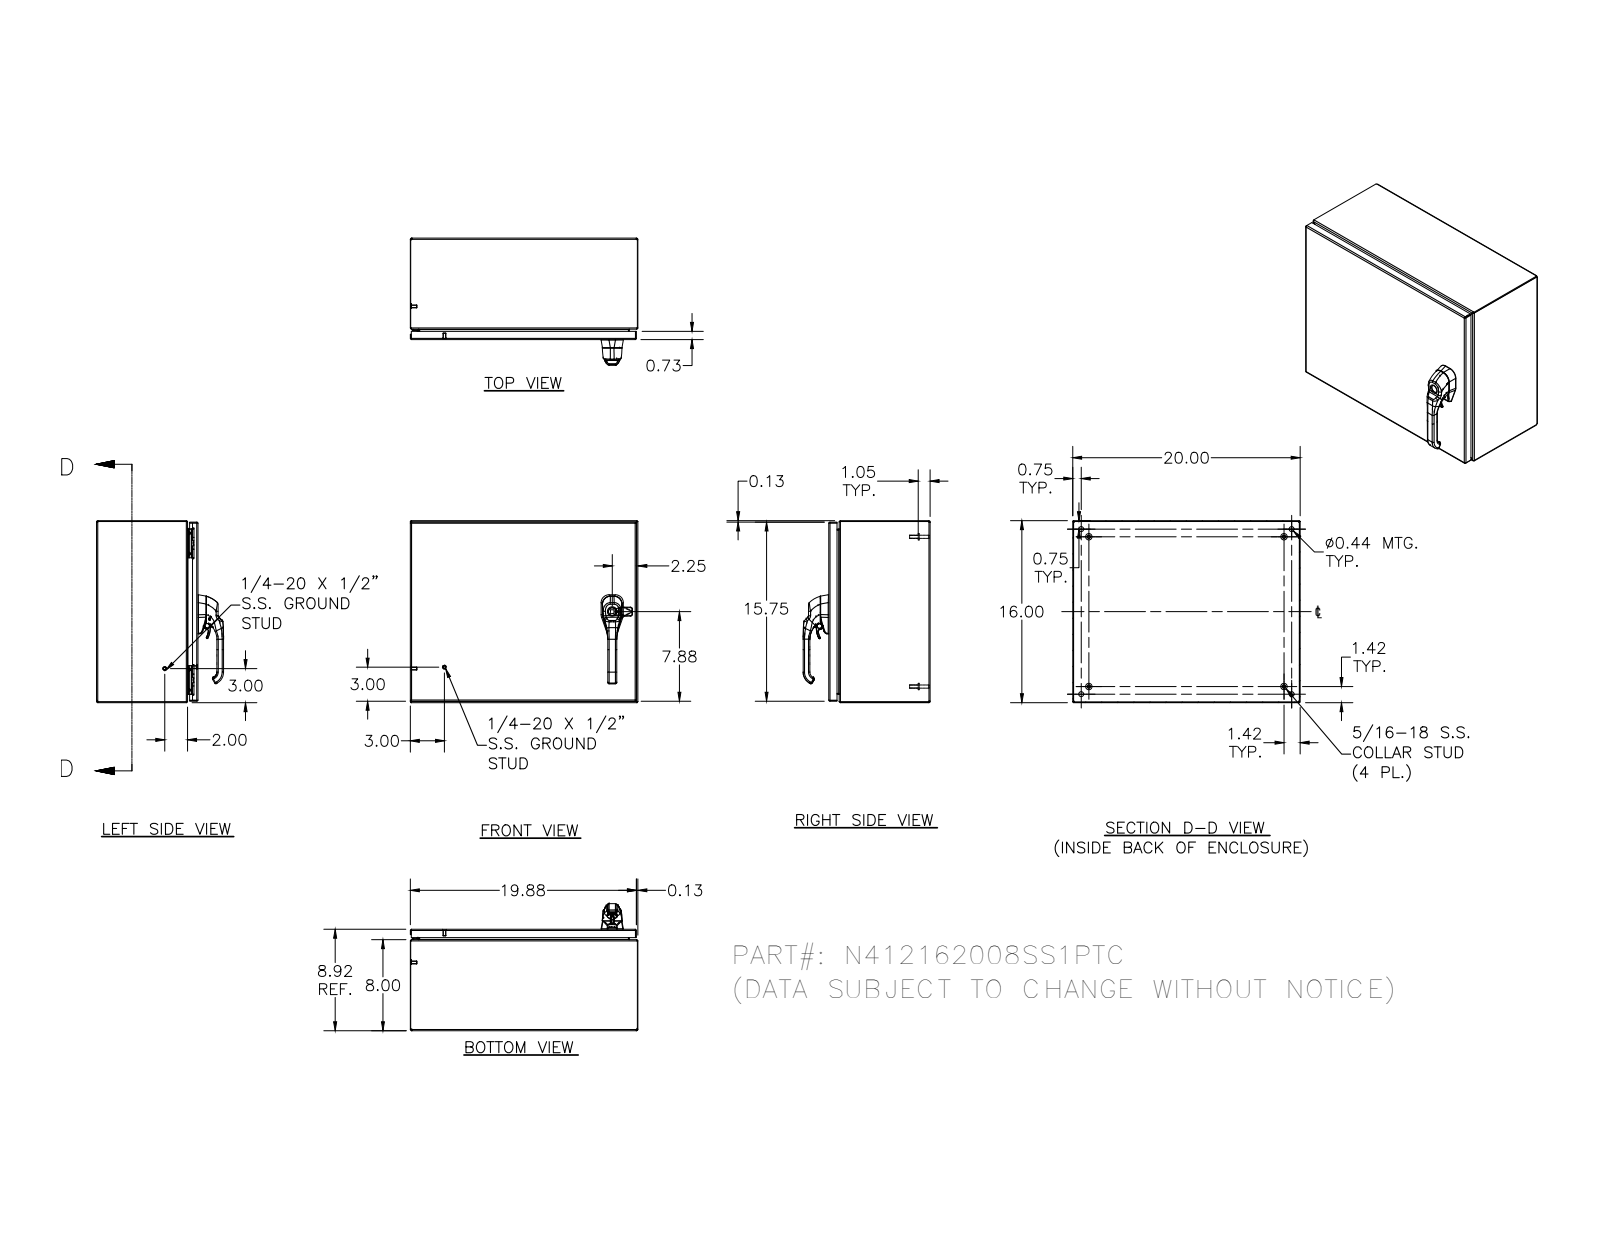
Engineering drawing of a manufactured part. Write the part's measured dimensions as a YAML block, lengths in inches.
part_name: "N412162008SS1PTC; N412162008SS1PTCBKP; N4121620SS1PTCLID; HFW328176 (+8 more)"
step_written_by: "Autodesk Inventor 2012 (AUTOMOTIVE_DESIGN)"
units: inches
bodies: {solids: 41, faces: 2782, planar: 882, cylindrical: 1035, other: 865}
overall_size: [20, 16, 11.166]
volume: 108
surface_area: 2837
round_holes:
  - {diameter: 0.093, count: 4}
  - {diameter: 0.152, count: 4}
  - {diameter: 0.167, count: 4}
  - {diameter: 0.172, count: 4}
  - {diameter: 0.188, count: 4}
  - {diameter: 0.437, count: 4}
  - {diameter: 0.213, count: 3}
  - {diameter: 0.281, count: 3}
  - {diameter: 0.156, count: 2}
  - {diameter: 0.315, count: 2}
  - {diameter: 0.402, count: 2}
  - {diameter: 0.413, count: 2}
round_bosses_or_shafts:
  - {diameter: 0.25, count: 10}
  - {diameter: 0.563, count: 4}
  - {diameter: 0.36, count: 4}
  - {diameter: 0.32, count: 4}
  - {diameter: 0.3, count: 4}
  - {diameter: 0.275, count: 4}
  - {diameter: 0.256, count: 4}
  - {diameter: 0.164, count: 4}
partial_cylinders:
  - {radius: 0.02, count: 173}
  - {radius: 0.012, count: 101}
  - {radius: 0.031, count: 30}
  - {radius: 0.05, count: 26}
  - {radius: 0.019, count: 21}
  - {radius: 0.105, count: 20}
  - {radius: 0.016, count: 18}
  - {radius: 0.079, count: 14}
face_to_face_distances: [0.074, 8.843, 15.926, 8.917, 8.769, 19.926, 16, 15.852, 19.852, 20]
hole_center_spacings: [11.996, 18.872, 0.017, 0.66, 12.656, 17.998, 18.152, 18.183]
